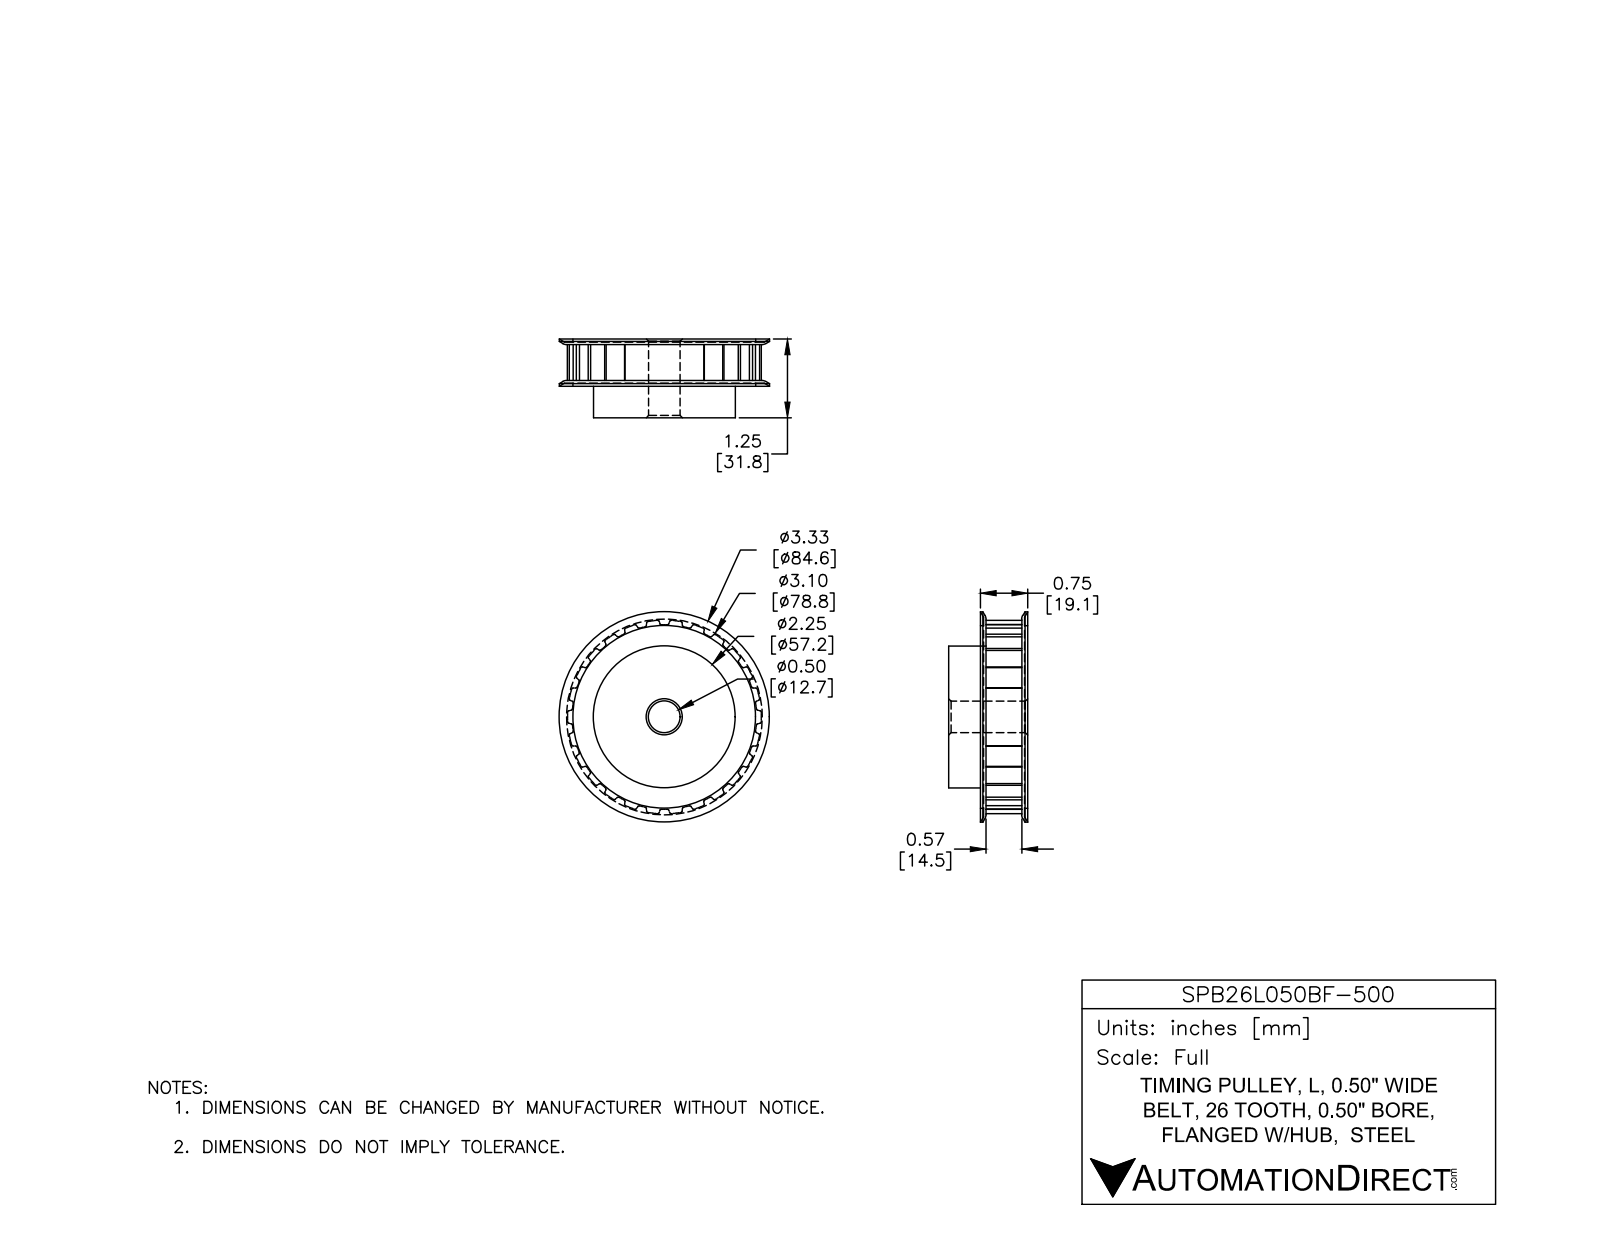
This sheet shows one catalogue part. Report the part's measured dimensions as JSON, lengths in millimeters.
{"part_name": "SPB26L050BF-500", "step_written_by": "SolidWorks 2015 (AUTOMOTIVE_DESIGN)", "units": "millimeters", "bodies": {"solids": 1, "faces": 252, "planar": 107, "cylindrical": 131, "other": 14}, "overall_size": [84.6, 84.6, 31.8], "volume_mm3": 120100, "surface_area_mm2": 21560, "round_holes": [[12.7, 1]], "round_bosses_or_shafts": [[84.6, 1], [57.2, 1]], "partial_cylinders_radius": [[0.5, 99], [39, 1]], "face_to_face_distances": [19.1, 31.8, 12.7, 2.3, 16.8, 78.1, 15, 14.5, 29.5, 78.1]}
